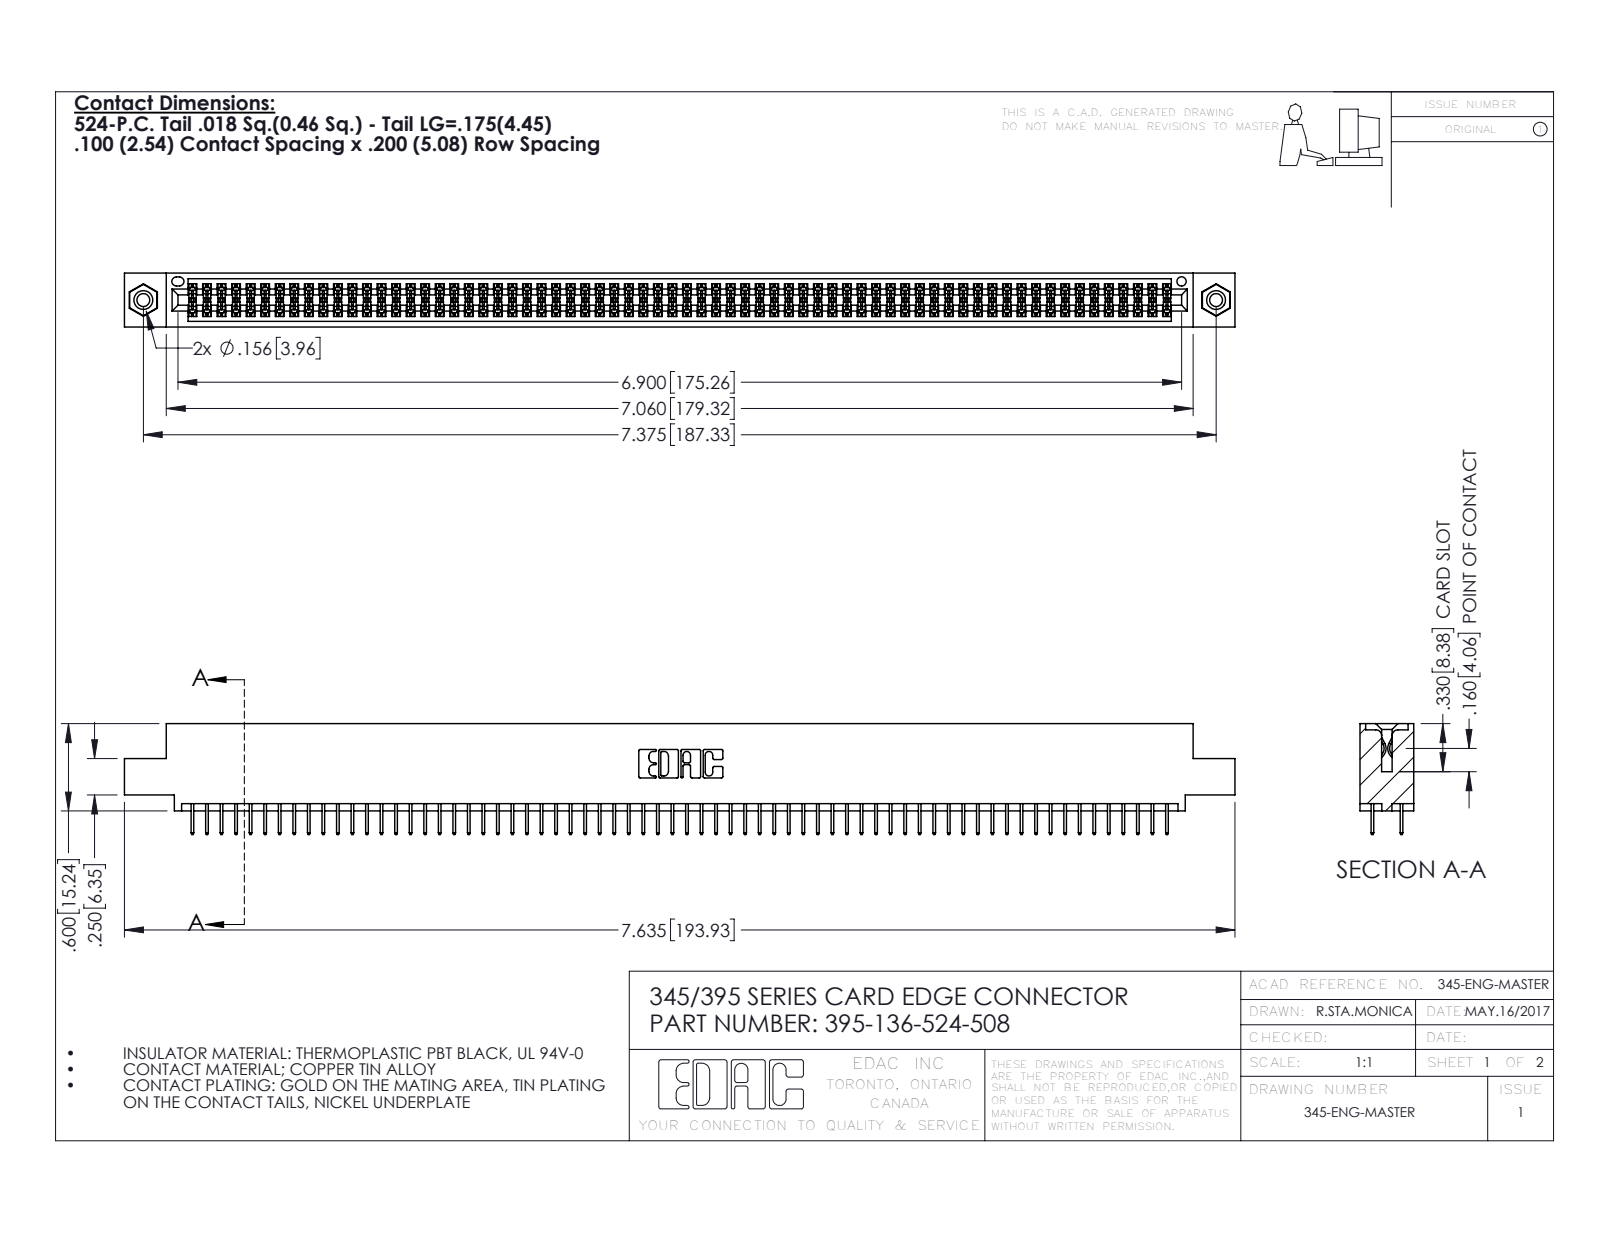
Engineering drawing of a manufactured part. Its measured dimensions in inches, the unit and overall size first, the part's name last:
Units: inches
Overall size (bounding box): 7.635 × 0.762 × 0.37
Round holes (diameter × count): ⌀0.089 ×2, ⌀0.125 ×2, ⌀0.156 ×2, ⌀0.064 ×1
Round bosses / shafts (diameter × count): ⌀0.155 ×2
Partial cylindrical surfaces — rounded edges, fillets, slot ends (radius × count): R0.006 ×204, R0.01 ×22, R0.007 ×6, R0.031 ×6, R0.026 ×3, R0.014 ×2, R0.019 ×2, R0.022 ×2
Main face-to-face distances: 0.072, 0.298, 0.2, 0.37, 0.098, 0.272, 0.025, 0.225, 0.072, 0.175
Hole centre spacings: 0.27, 7.139, 7.375
Volume: 1.147 in³ · Surface area: 43.16 in²
Bodies: 139 solids, 7534 faces (5420 planar, 2098 cylindrical, 16 other)
Part name (STEP PRODUCT): 345-250-001_345-250-003-102; 345-292-001_345-293-124; 345 Part_0.110 Offset - 0.156 Dia-TI; 395-136-524-508
STEP written by: SolidWorks 2016 (CONFIG_CONTROL_DESIGN)
